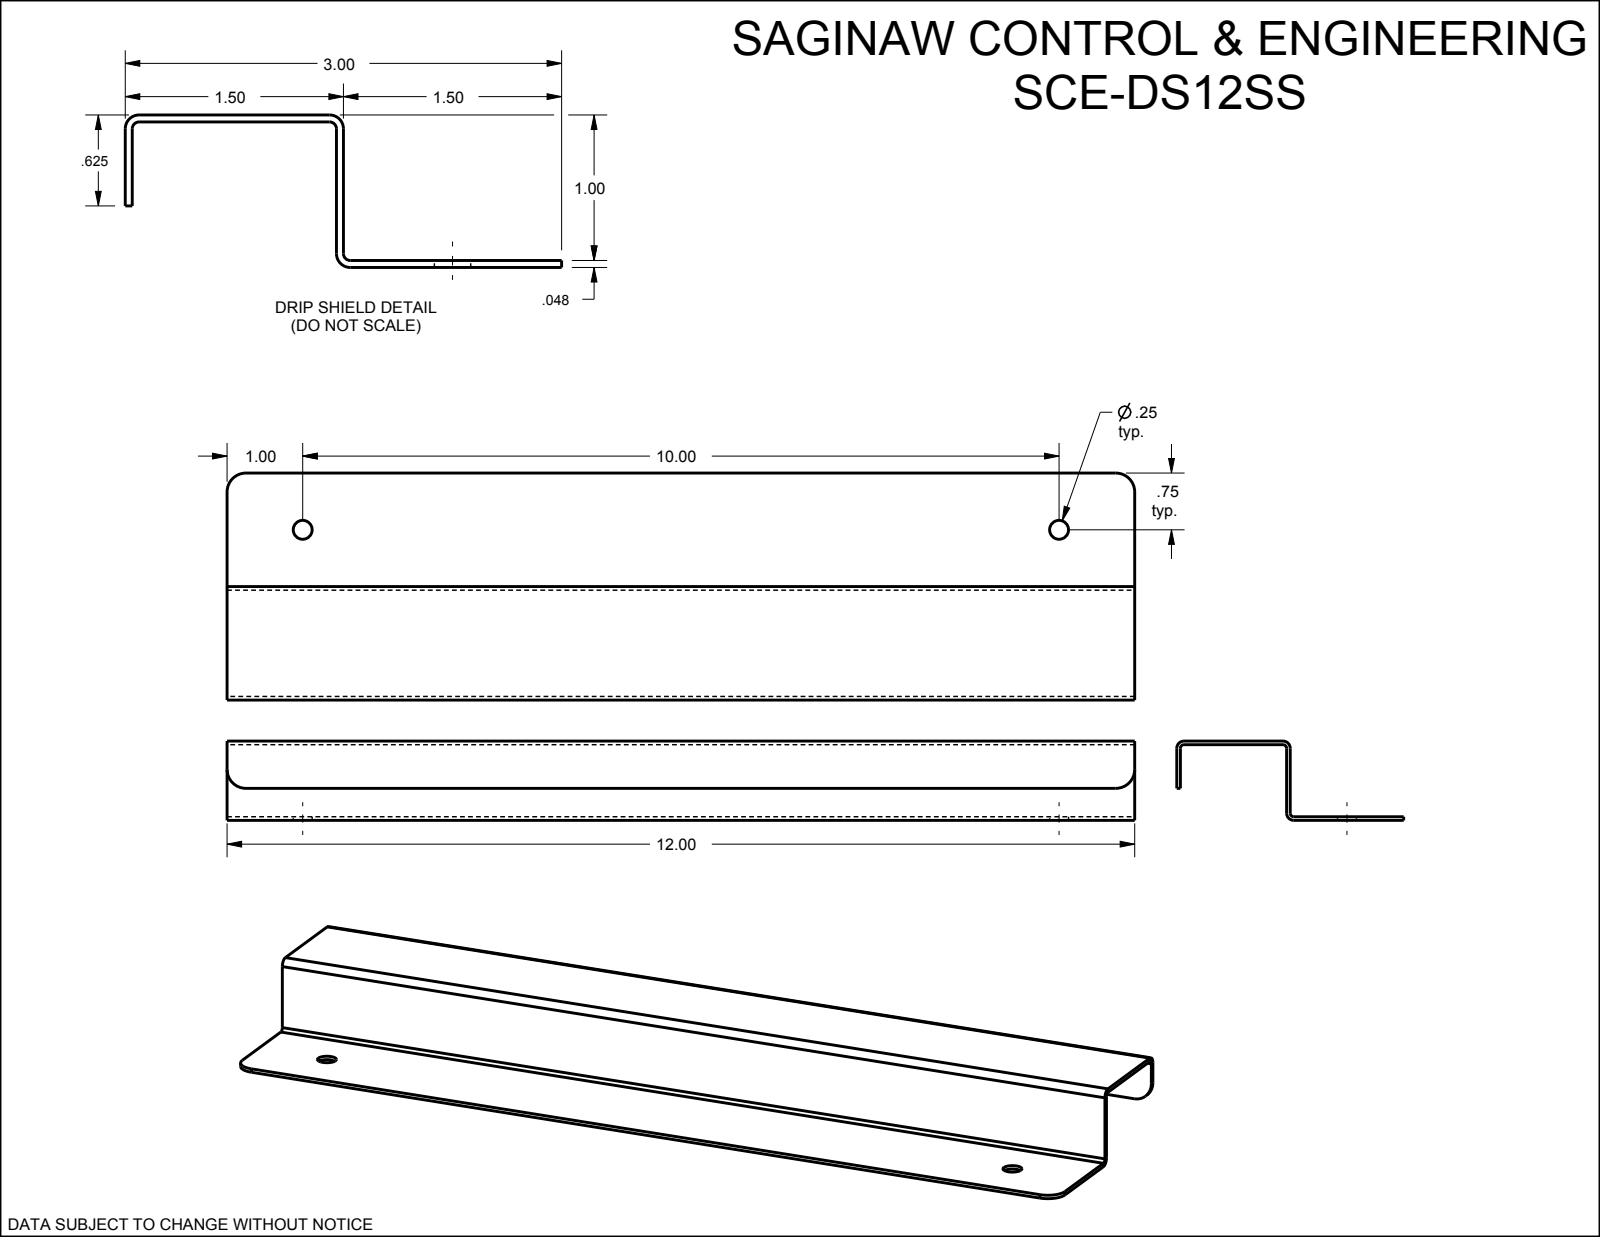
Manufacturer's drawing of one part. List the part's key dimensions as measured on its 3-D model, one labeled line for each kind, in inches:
Part name (STEP PRODUCT): SCE-DS12SS
STEP written by: SolidWorks 2019 (CONFIG_CONTROL_DESIGN)
Units: inches
Bodies: 1 solid, 24 faces (12 planar, 12 cylindrical, 0 other)
Overall size (bounding box): 12 × 3 × 1.048
Volume: 2.576 in³ · Surface area: 109 in²
Round holes (diameter × count): ⌀0.25 ×2
Partial cylindrical surfaces — rounded edges, fillets, slot ends (radius × count): R0.25 ×4, R0.047 ×3, R0.095 ×3
Main face-to-face distances: 0.048, 1, 1.048, 0.952, 1.452, 1.5, 1.404, 0.423, 0.375, 0.577
Hole centre spacings: 10
